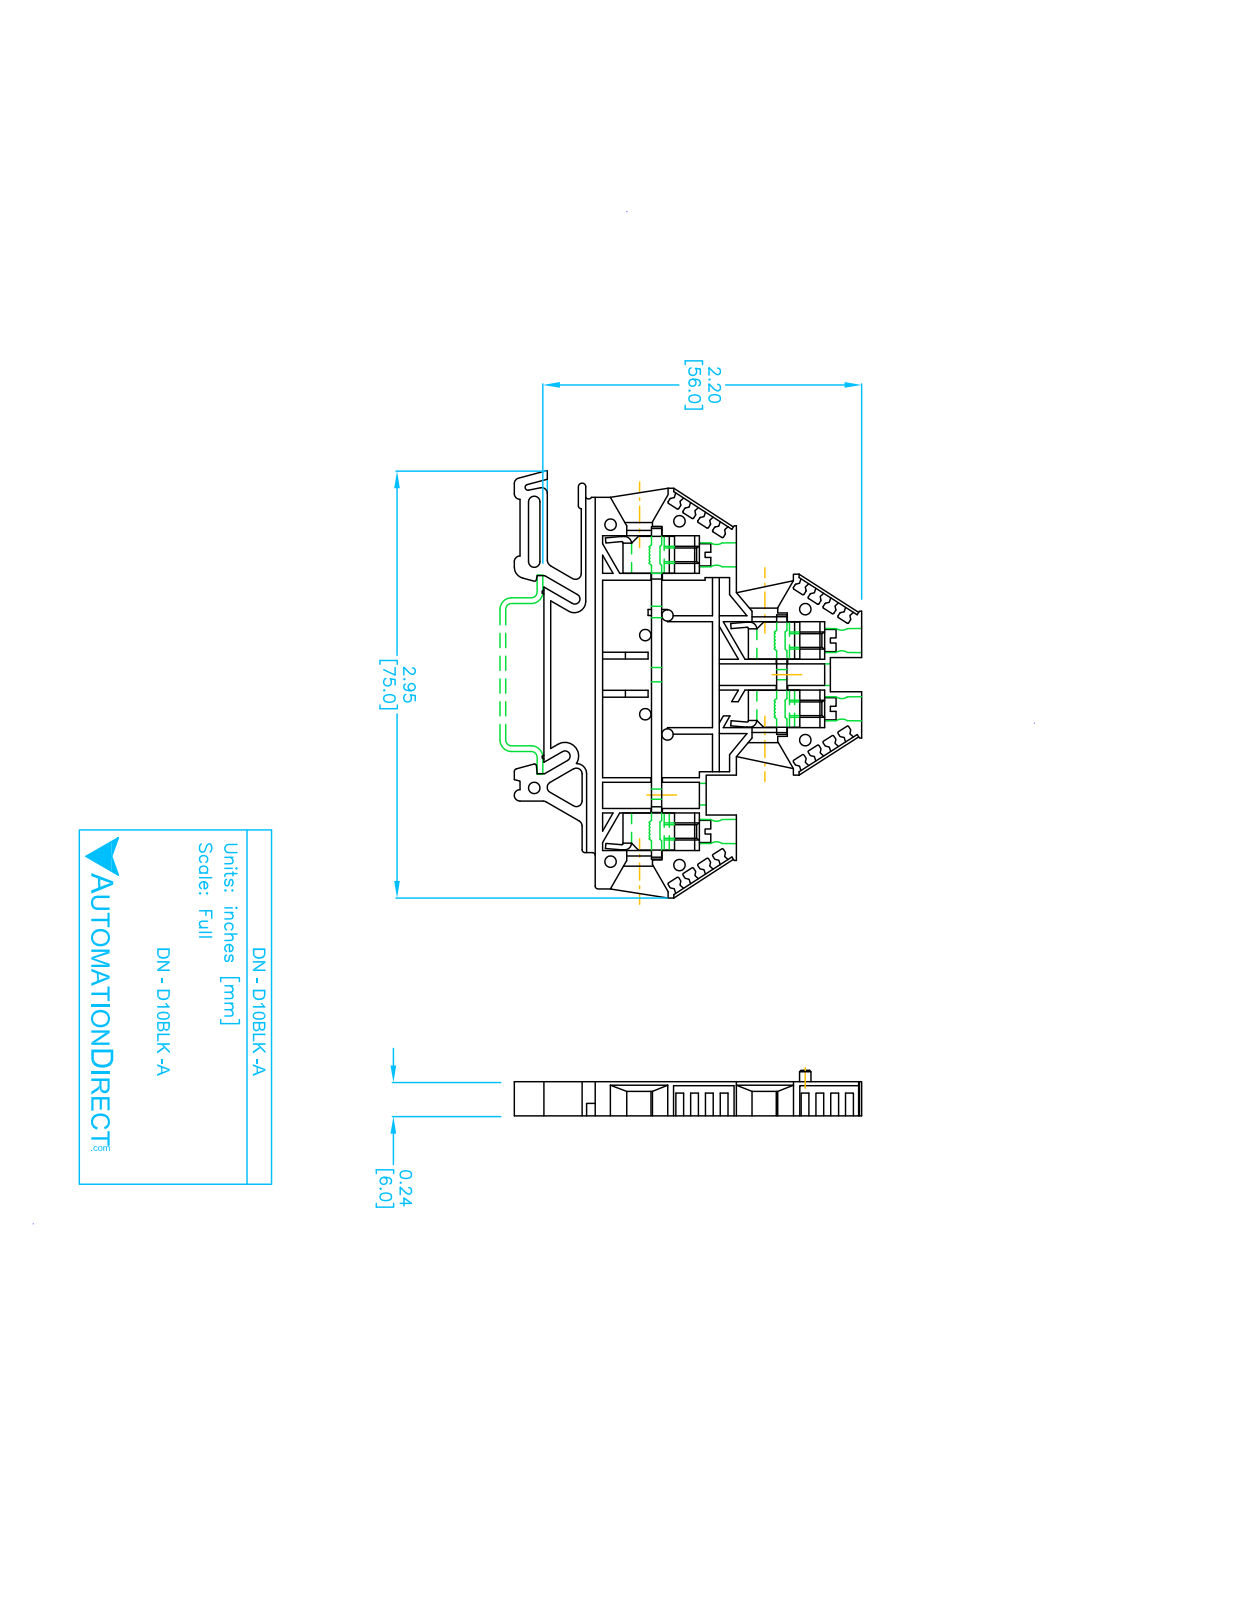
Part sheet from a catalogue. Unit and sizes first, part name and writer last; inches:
Units: inches
Overall size (bounding box): 2.957 × 2.402 × 0.236
Round holes (diameter × count): ⌀0.165 ×4, ⌀0.079 ×1
Round bosses / shafts (diameter × count): ⌀0.146 ×4
Partial cylindrical surfaces — rounded edges, fillets, slot ends (radius × count): R0.008 ×64, R0.039 ×13, R0.02 ×6, R0.012 ×2, R0.035 ×2, R0.075 ×2, R0.079 ×2, R0.004 ×1
Main face-to-face distances: 0.236, 0.079, 0.157, 0.354, 0.059, 0.024, 0.031, 0.047, 0.976, 0.071
Hole centre spacings: 0.472, 0.593, 0.848, 1.065, 1.321, 1.913
Volume: 0.9 in³ · Surface area: 14.85 in²
Bodies: 1 solid, 402 faces (261 planar, 141 cylindrical, 0 other)
Part name (STEP PRODUCT): DN-D10BLK-A
STEP written by: SolidWorks 2017 (AUTOMOTIVE_DESIGN)
